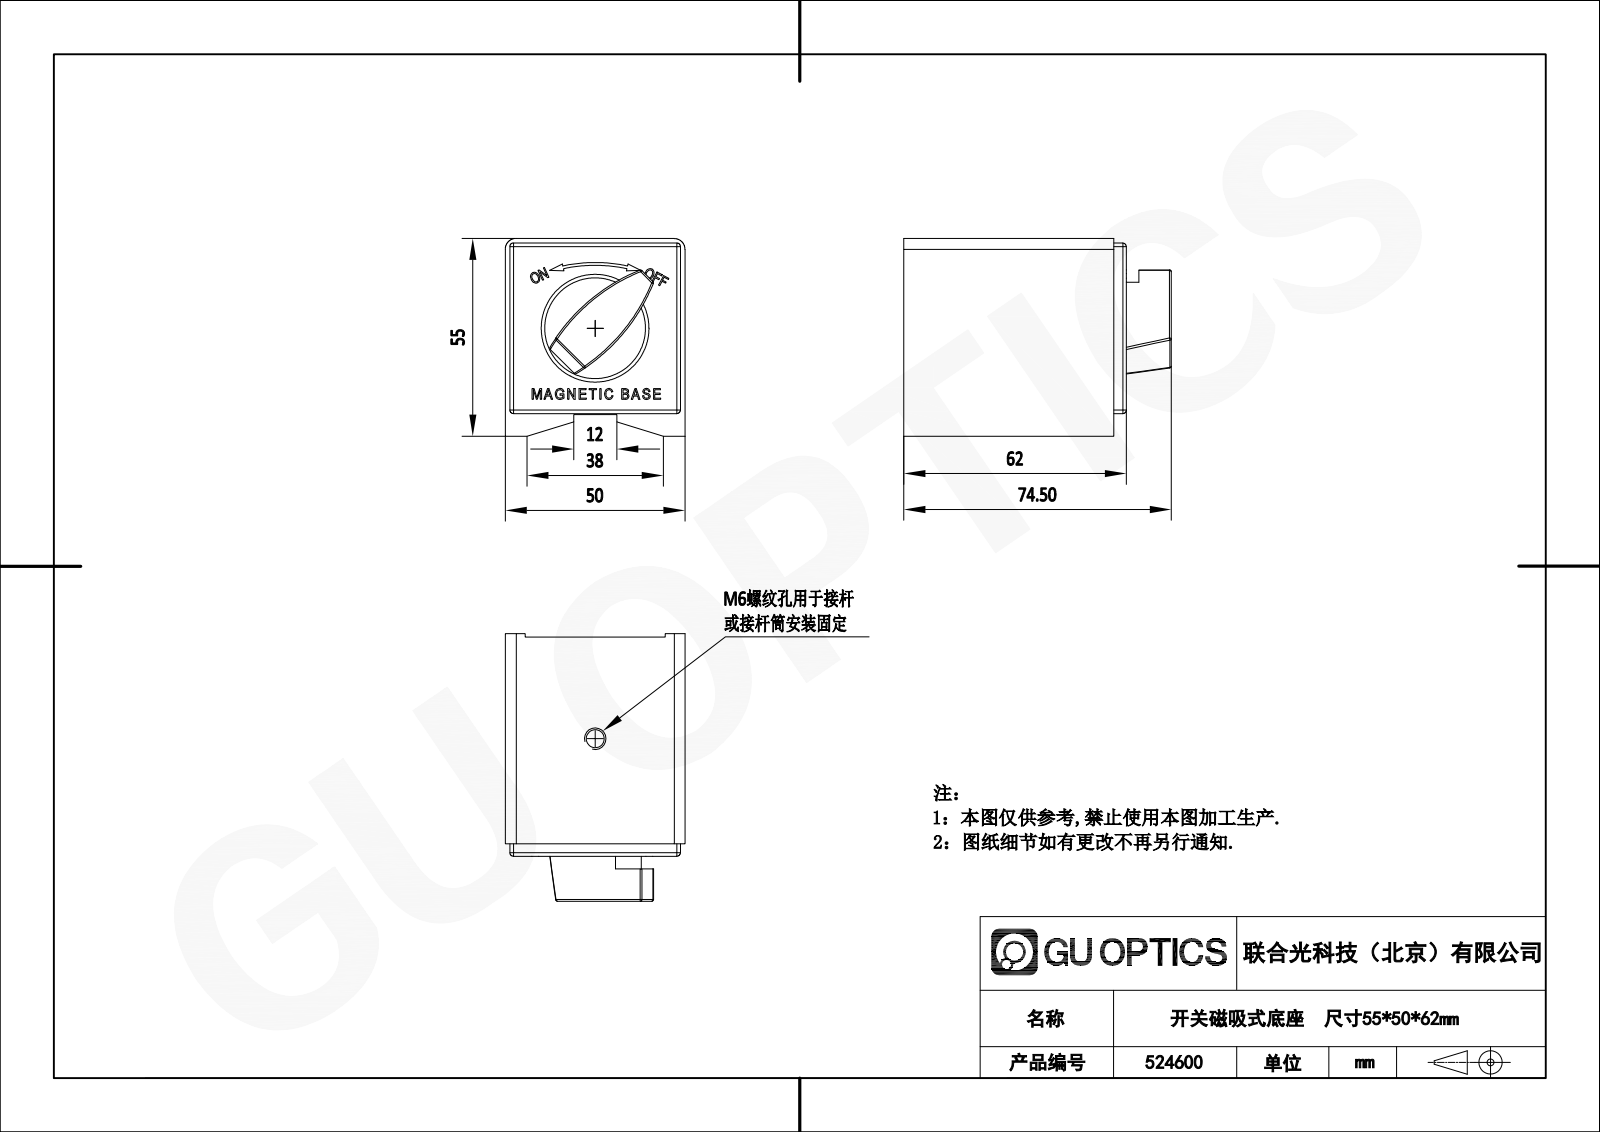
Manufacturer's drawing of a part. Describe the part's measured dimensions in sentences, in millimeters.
The part is named "524600". Its 3-D file was written by "SolidWorks 2020 (CONFIG_CONTROL_DESIGN)". It is 1 solid with 129 faces: 73 planar, 21 cylindrical and 35 other. Overall it measures 74.5 by 55 by 50 millimeters. Its volume is 163 159 cubic millimeters and its surface area 19 847 square millimeters. Round holes: 1 of diameter 5, 1 of diameter 30. Round bosses or shafts: 1 of diameter 28. Partial cylindrical surfaces (rounded edges, fillets, slot ends): 8 of radius 1, 4 of radius 0.5, 2 of radius 3, 2 of radius 52, 1 of radius 42.5, 1 of radius 43.3. The main face-to-face distances are 50, 61, 55, 6, 49, 1, 62, 3.5, 58.5, 57.5.
